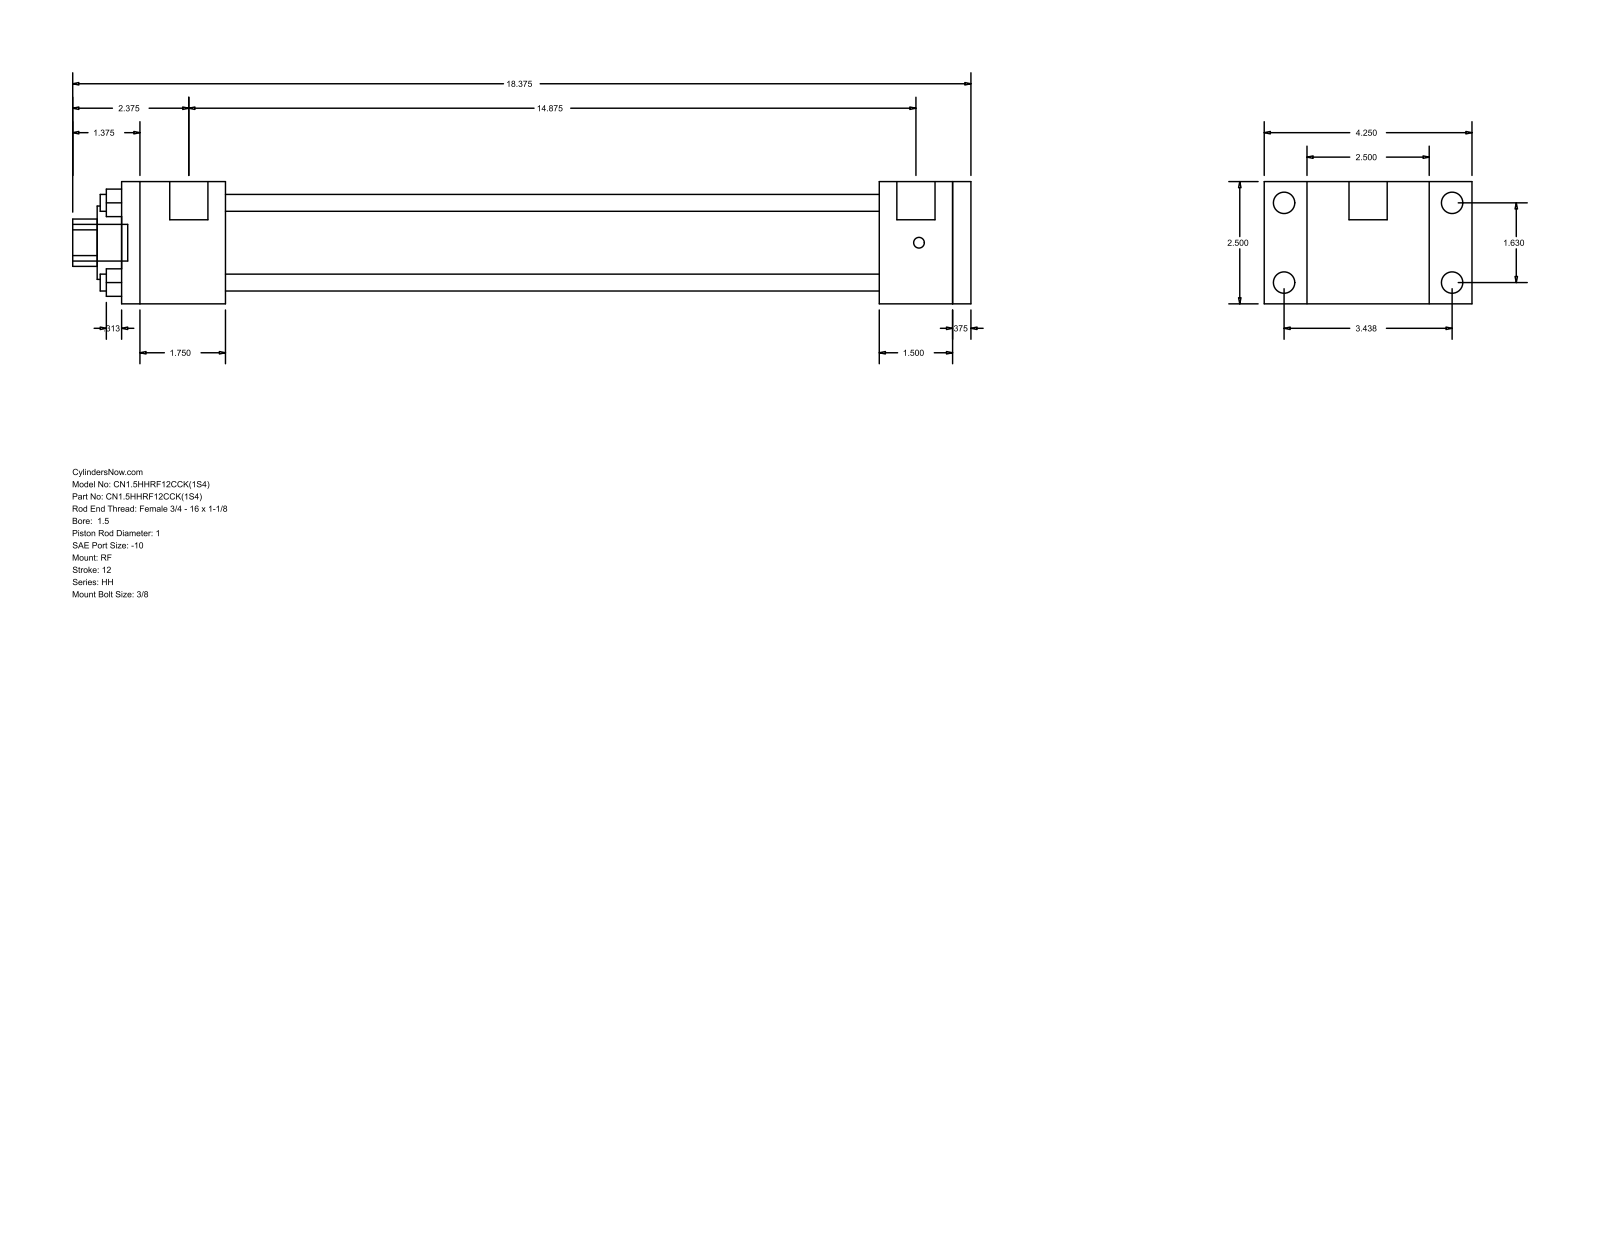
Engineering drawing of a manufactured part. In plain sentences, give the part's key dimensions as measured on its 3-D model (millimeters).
The part is named "HH_RF__0150_1". Its 3-D file was written by "GSSL Pune (CONFIG_CONTROL_DESIGN)". It is 0 solids with 92 faces: 64 planar, 28 cylindrical and 0 other. Overall it measures 466.73 by 107.95 by 63.5 millimeters. Round holes: 4 of diameter 8.76, 1 of diameter 25.4, 1 of diameter 38.1, 1 of diameter 44.45. Round bosses or shafts: 4 of diameter 11.13, 4 of diameter 5.56, 2 of diameter 19.84, 1 of diameter 19.05. Partial cylindrical surfaces (rounded edges, fillets, slot ends): 1 of radius 12.29. The main face-to-face distances are 63.5, 9.53, 339.72, 377.82, 387.35, 38.1, 47.63, 53.98, 393.7, 431.8. The hole center spacings are 29.27, 41.4, 58.55.
